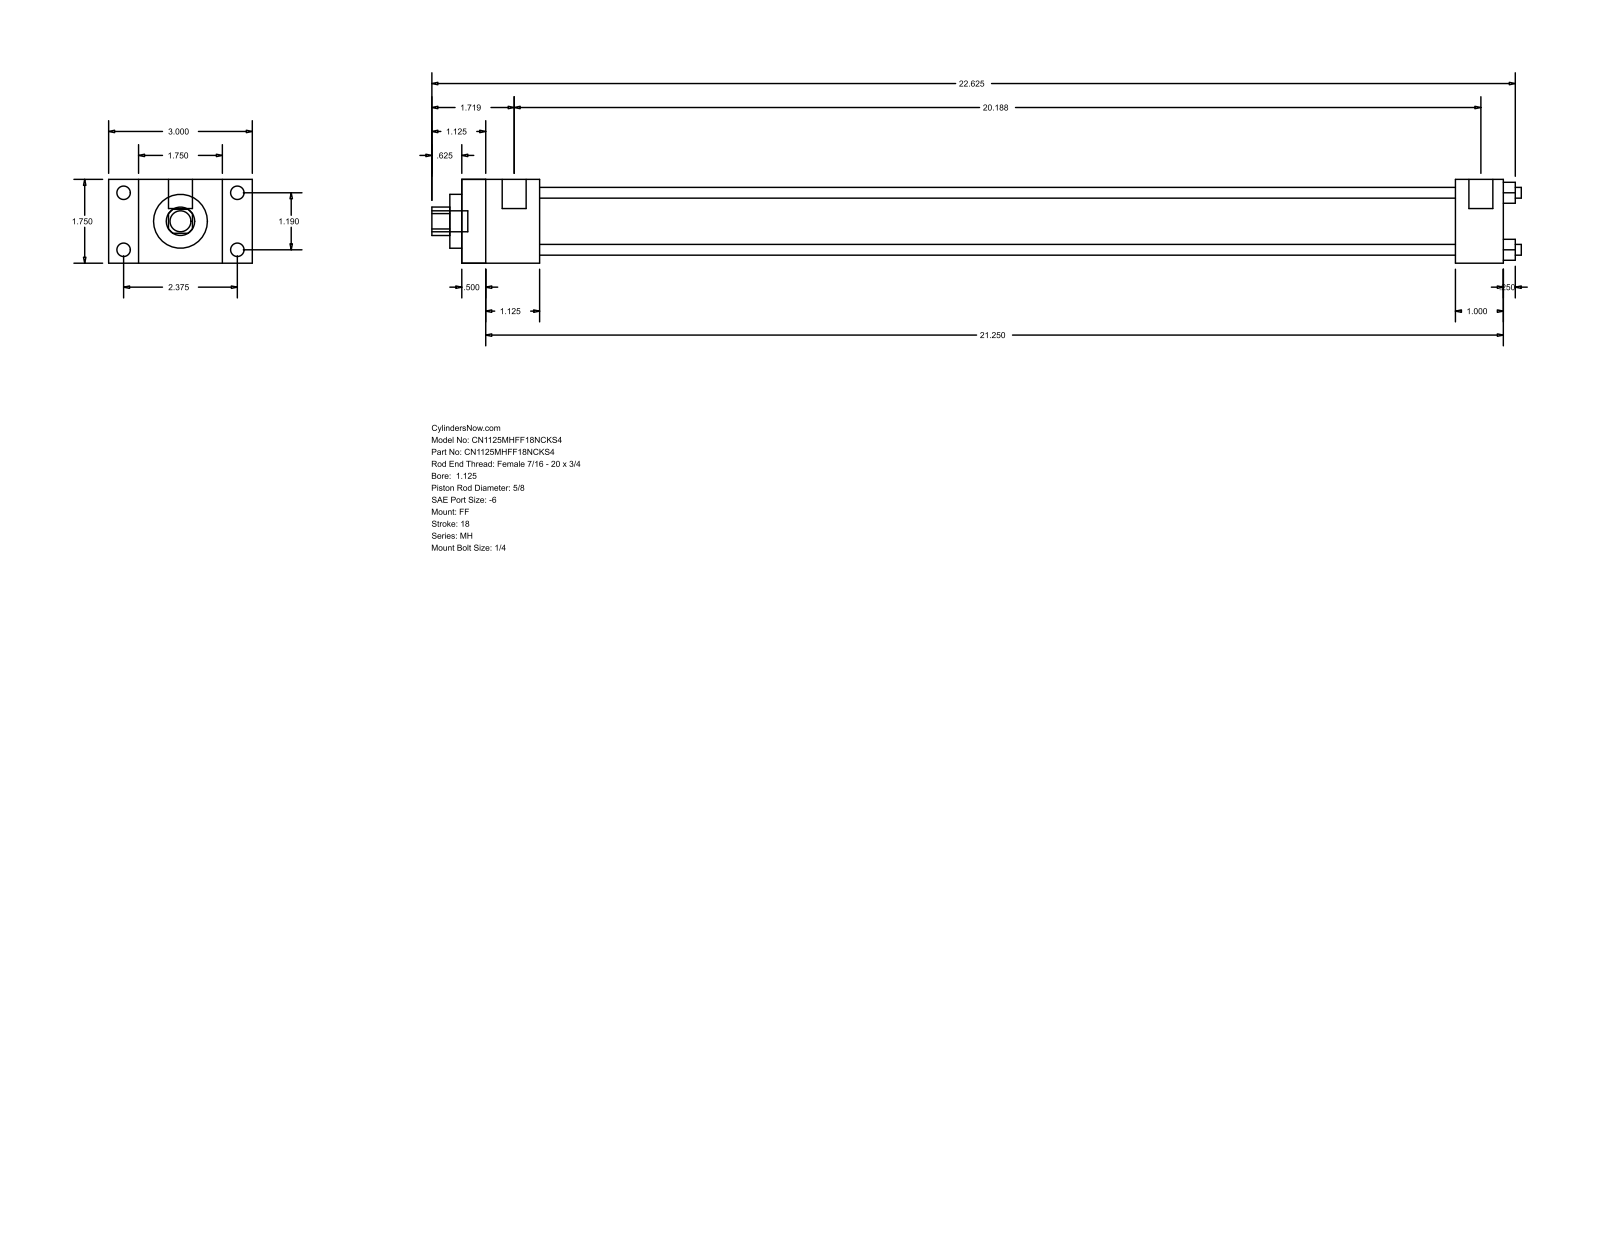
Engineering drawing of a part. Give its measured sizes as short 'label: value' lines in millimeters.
name: MH_FF__0112_0.625
written by: GSSL Pune (CONFIG_CONTROL_DESIGN)
unit: mm
bodies: 0 solids, 92 faces (64 planar, 28 cylindrical, 0 other)
size: 577.85 × 76.2 × 44.45
holes: 4× ⌀5.71, 1× ⌀15.88, 1× ⌀28.57, 1× ⌀34.92
bosses: 4× ⌀7.14, 4× ⌀5.56, 2× ⌀12.7, 1× ⌀11.11
rounds: 1× R7.54
face distances: 44.46, 552.45, 15.87, 12.69, 539.76, 60.33, 28.58, 41.27, 527.04, 514.35
hole spacings: 21.37, 30.22, 42.74
